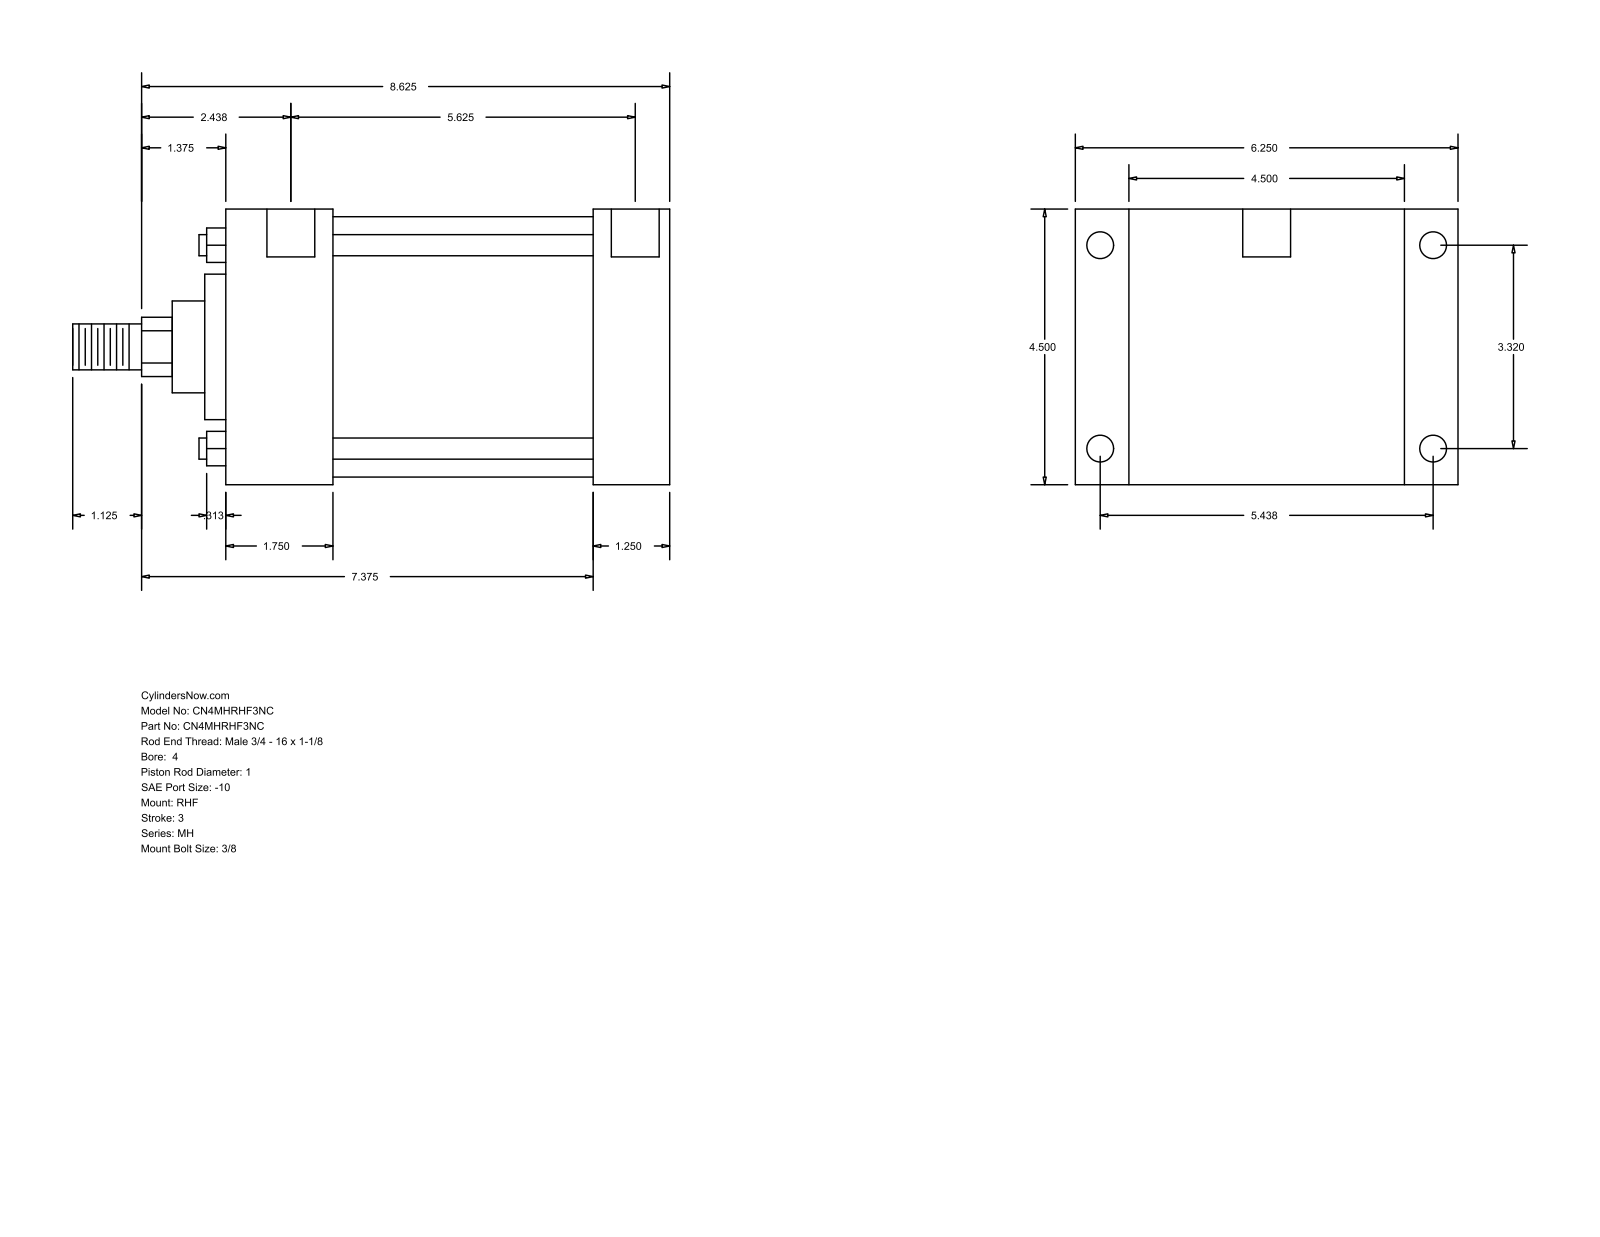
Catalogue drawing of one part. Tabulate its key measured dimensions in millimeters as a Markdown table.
| quantity | value |
| --- | --- |
| part name | MH_RHF__0400_1 |
| STEP written by | GSSL Pune (CONFIG_CONTROL_DESIGN) |
| units | millimeters |
| bodies | 0 solids, 90 faces (61 planar, 29 cylindrical, 0 other) |
| overall size | 247.65 × 158.75 × 114.3 |
| round holes (diameter × count) | 8.73 × 4, 11.13 × 4, 19.84 × 2 |
| round bosses / shafts (diameter × count) | 8.76 × 4, 107.95 × 1, 60.33 × 1, 38.1 × 1, 25.4 × 1, 19.05 × 1 |
| partial cylindrical surfaces (radius × count) | 12.29 × 1 |
| main face-to-face distances | 114.3, 184.15, 152.4, 31.75, 22.23, 136.53, 44.46, 107.94, 139.69, 158.76 |
| hole center spacings | 84.32, 138.12, 146.05, 161.82, 1.58, 1.59, 142.88, 144.46 |
